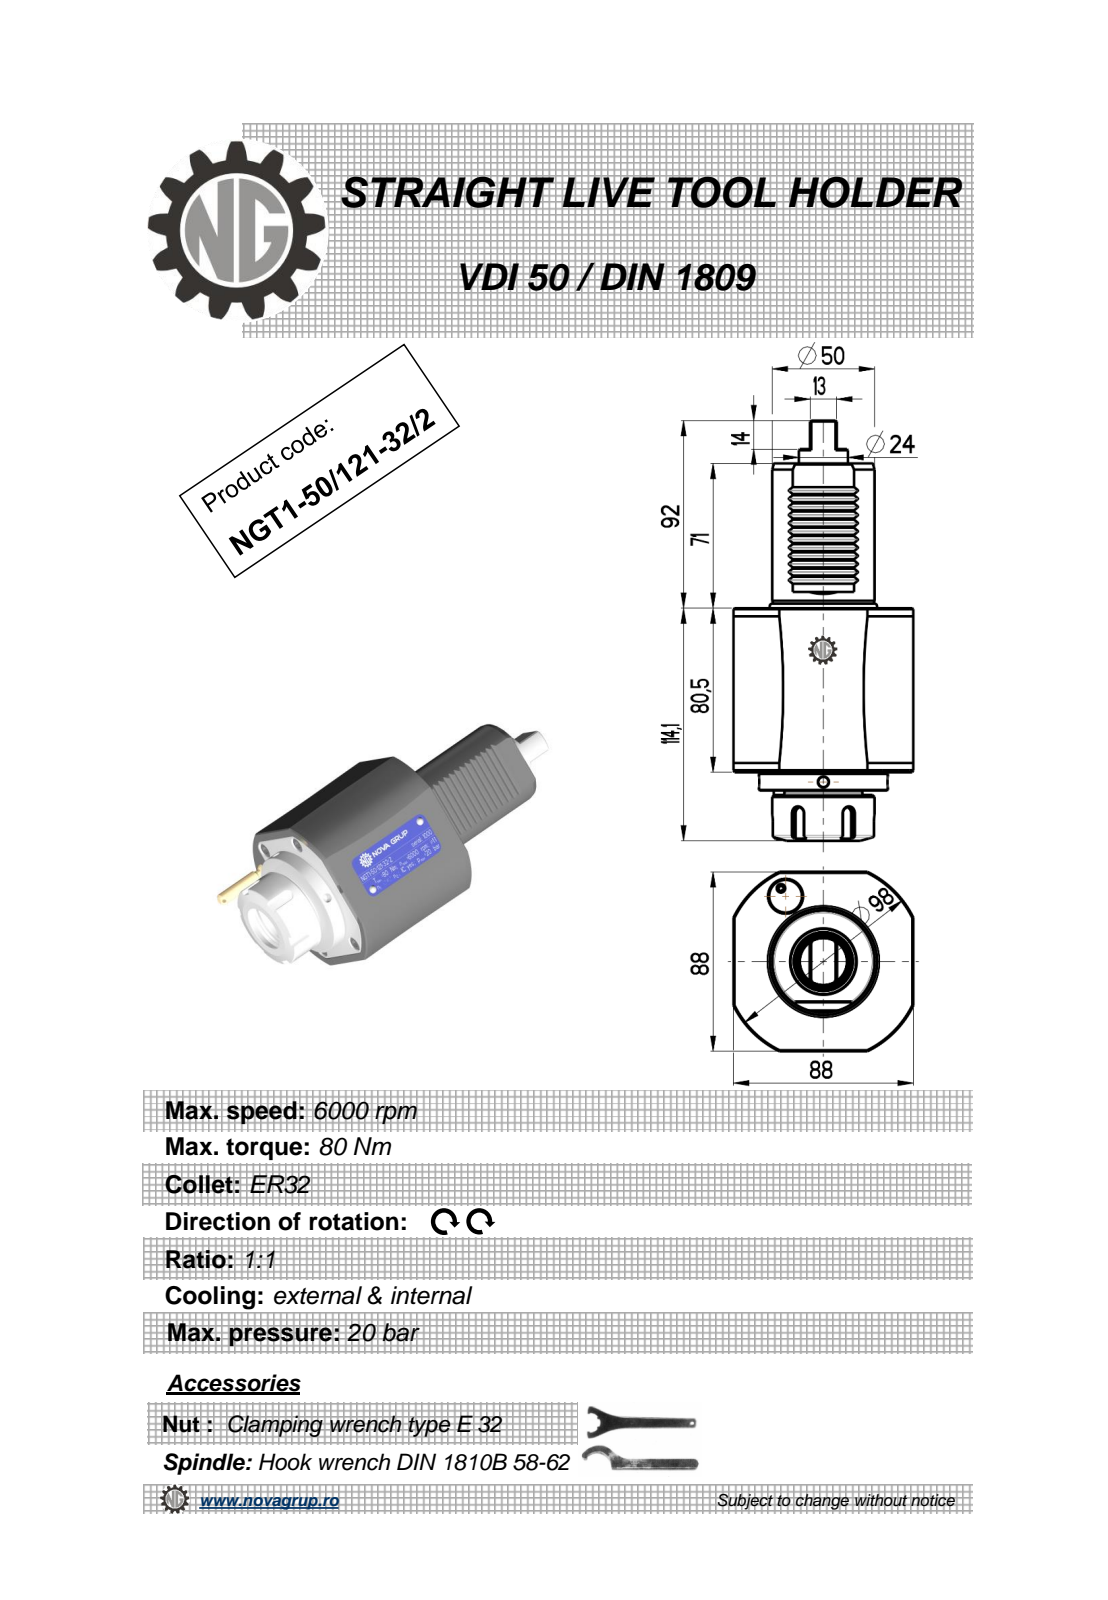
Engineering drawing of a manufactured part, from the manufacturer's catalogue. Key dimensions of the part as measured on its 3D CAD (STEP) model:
Part name (STEP PRODUCT): NGT1_50_121_32_1
STEP written by: PRO/ENGINEER BY PARAMETRIC TECHNOLOGY CORPORATION, 2010280 (CONFIG_CONTROL_DESIGN)
Units: millimetres
Bodies: 1 solid, 261 faces (114 planar, 59 cylindrical, 88 other)
Overall size (bounding box): 206.1 × 88 × 88
Volume: 763 937 mm³ · Surface area: 62 053 mm²
Round holes (diameter × count): ⌀5 ×2, ⌀2.5 ×1, ⌀3 ×1, ⌀27 ×1
Round bosses / shafts (diameter × count): ⌀63 ×1, ⌀51.1 ×1, ⌀50 ×1, ⌀41 ×1, ⌀24 ×1, ⌀9 ×1, ⌀7 ×1, ⌀5 ×1
Partial cylindrical surfaces — rounded edges, fillets, slot ends (radius × count): R0.3 ×12, R3 ×5, R0.8 ×2, R49 ×1
Main face-to-face distances: 88, 80.5, 9, 89.5, 71, 151.5, 160.5, 2.83, 81, 152
Hole centre spacings: 41.5
